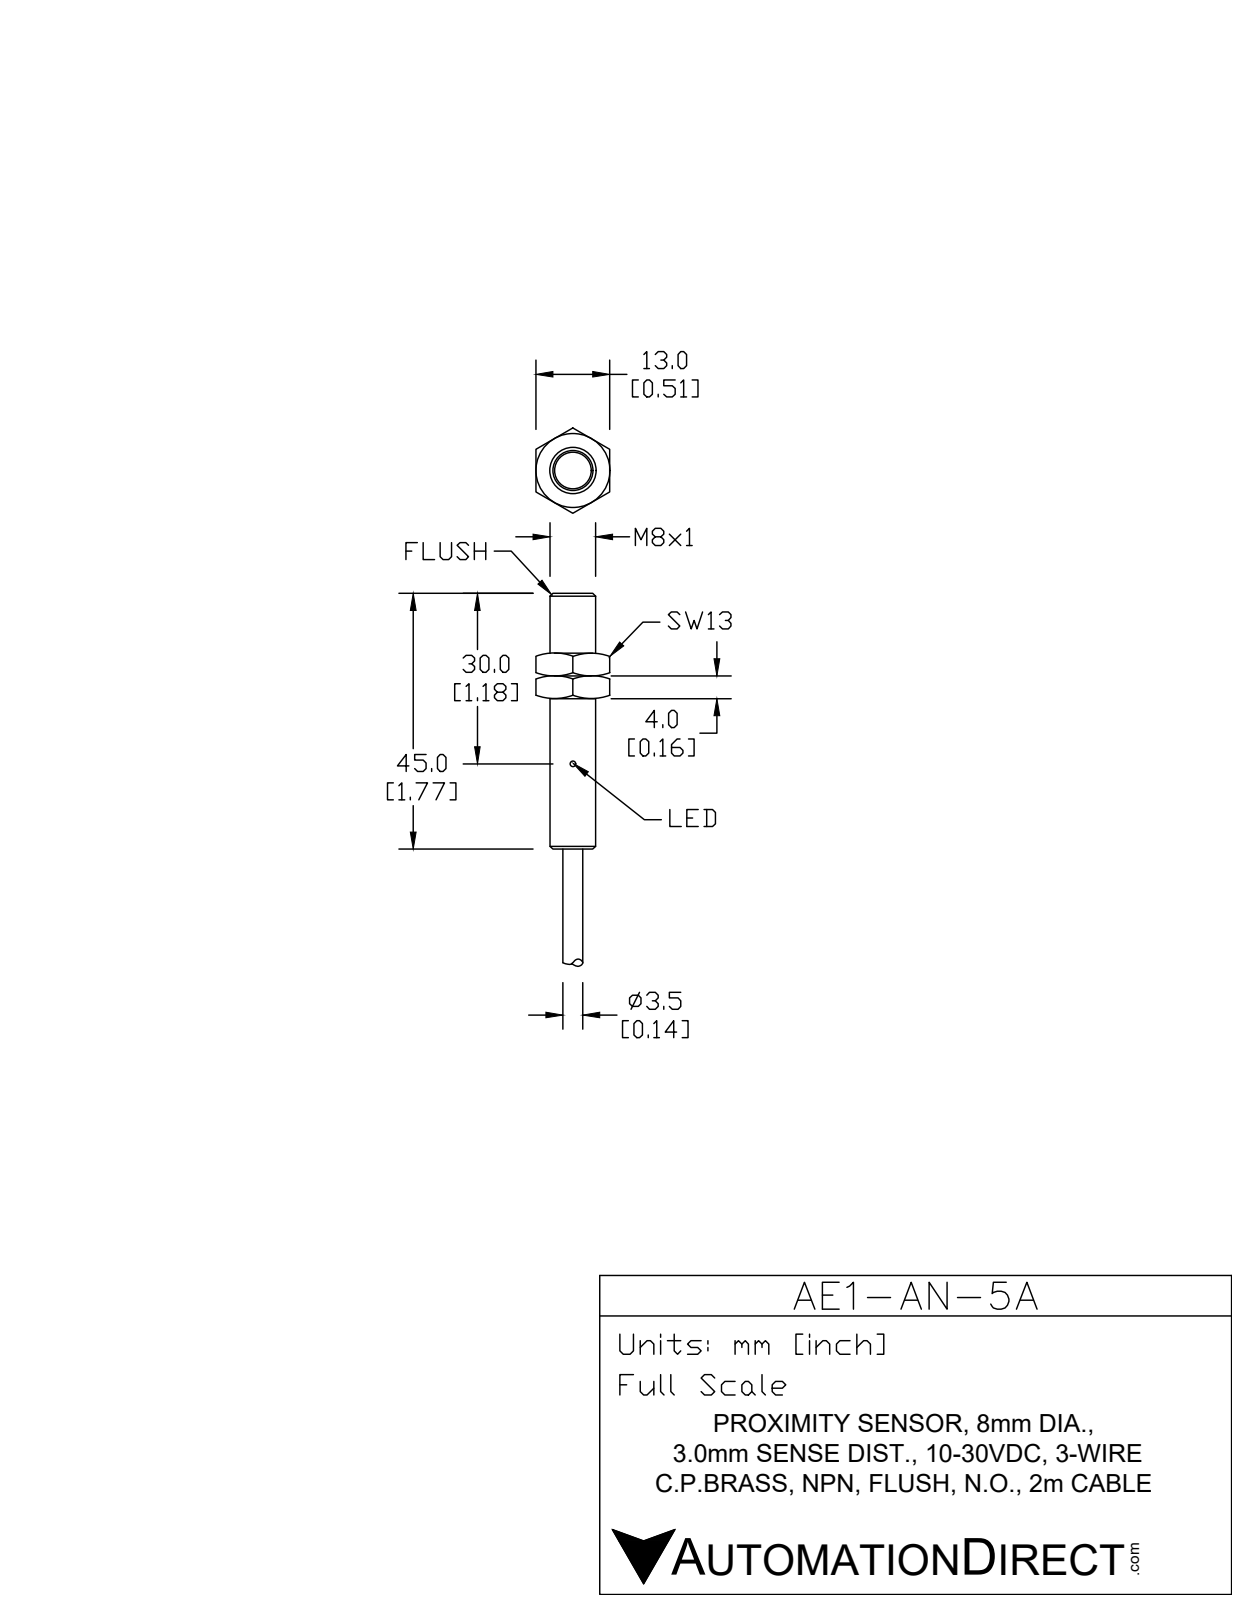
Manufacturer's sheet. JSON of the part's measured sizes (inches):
{"part_name": "AE1-AN-5A", "step_written_by": "SolidWorks 2017 (AUTOMOTIVE_DESIGN)", "units": "inches", "bodies": {"solids": 1, "faces": 10, "planar": 4, "cylindrical": 3, "other": 3}, "overall_size": [2.803, 0.315, 0.315], "volume_in3": 0.17, "surface_area_in2": 2.53, "round_bosses_or_shafts": [[0.315, 1], [0.256, 1], [0.197, 1]], "face_to_face_distances": [2.803, 1.791, 1.012, 1.772, 0.02, 1.031]}
